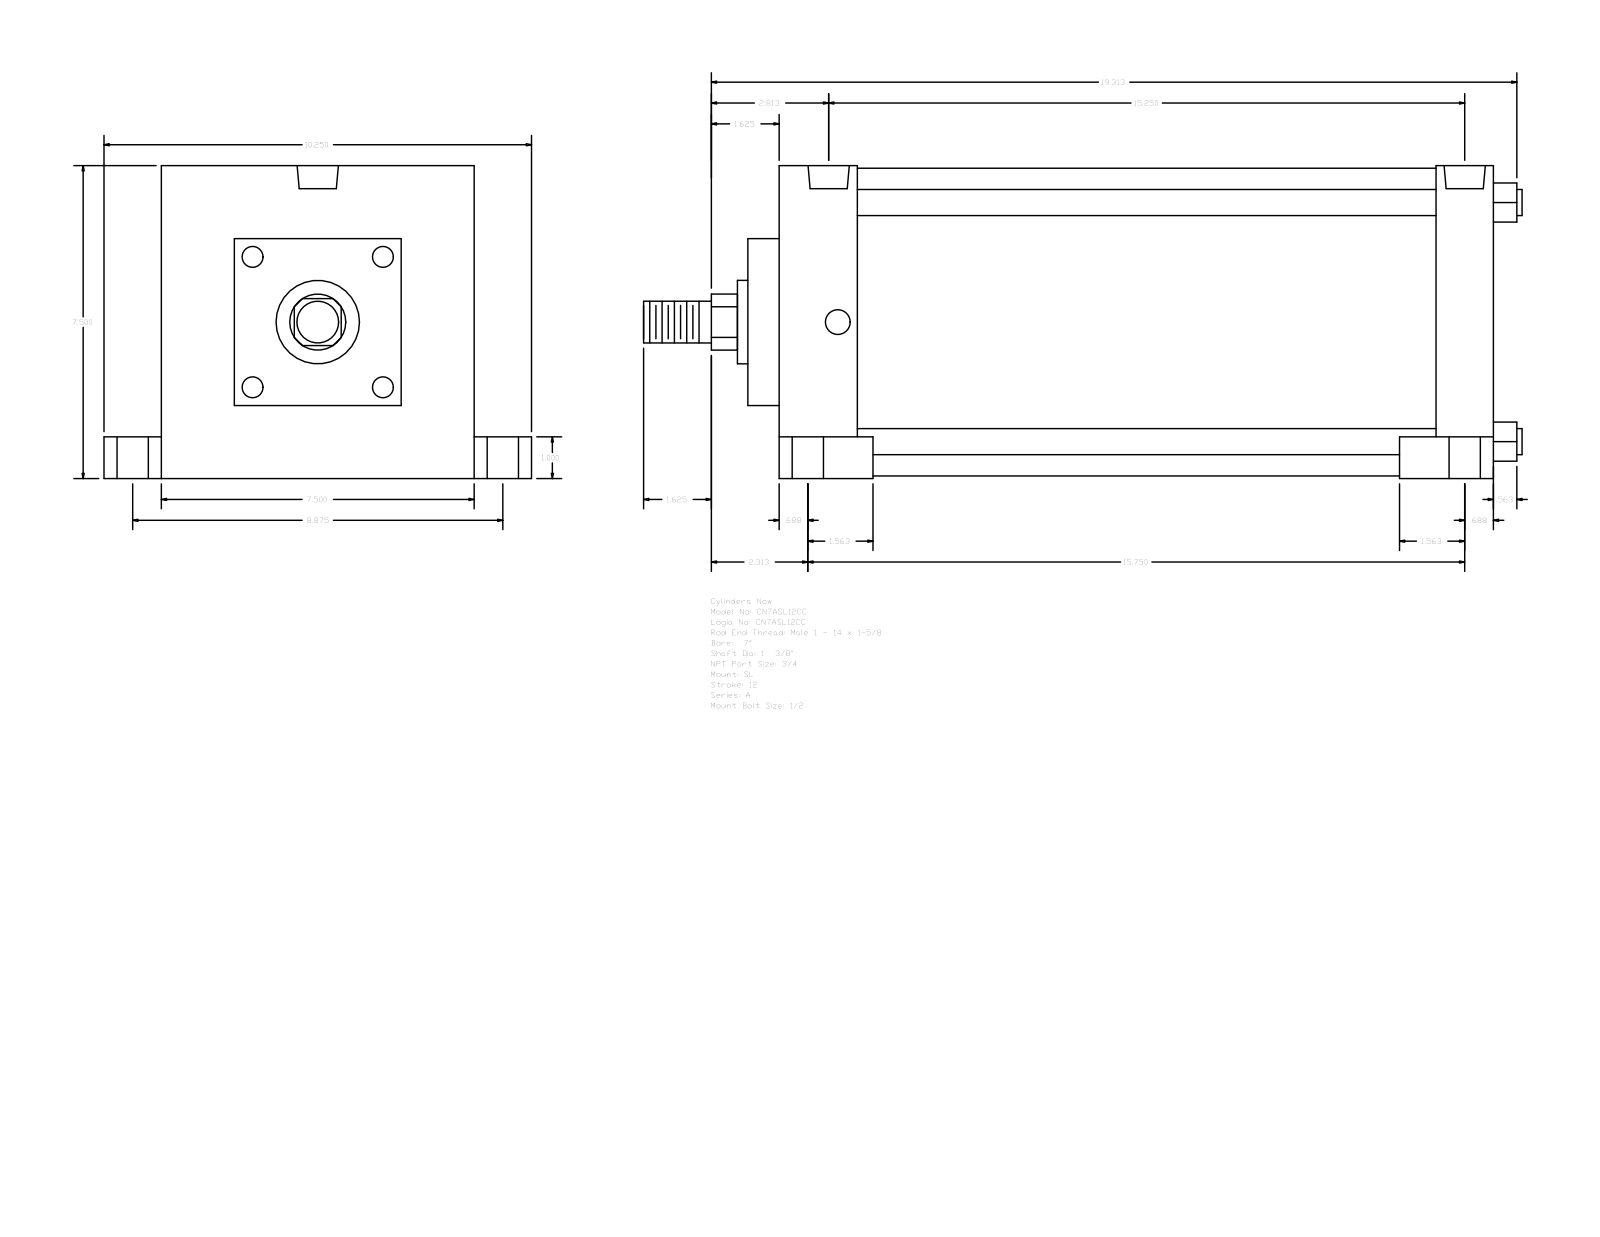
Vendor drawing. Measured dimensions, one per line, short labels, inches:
name: A_SL__0700_1.375
written by: GSSL Pune (CONFIG_CONTROL_DESIGN)
unit: in
bodies: 0 solids, 117 faces (85 planar, 32 cylindrical, 0 other)
size: 21.063 × 10.25 × 7.5
holes: 4× ⌀0.594, 4× ⌀0.75, 4× ⌀1, 2× ⌀0.989
bosses: 4× ⌀0.625, 1× ⌀7.375, 1× ⌀2, 1× ⌀1.375, 1× ⌀1
rounds: 1× R0.672
face distances: 7.5, 17.125, 1.375, 0.75, 17.875, 2.625, 1.875, 15.25, 16.5, 15.75
hole spacings: 0.219, 4.437, 4.443, 4.465, 4.495, 8.875, 14.812, 15.031
